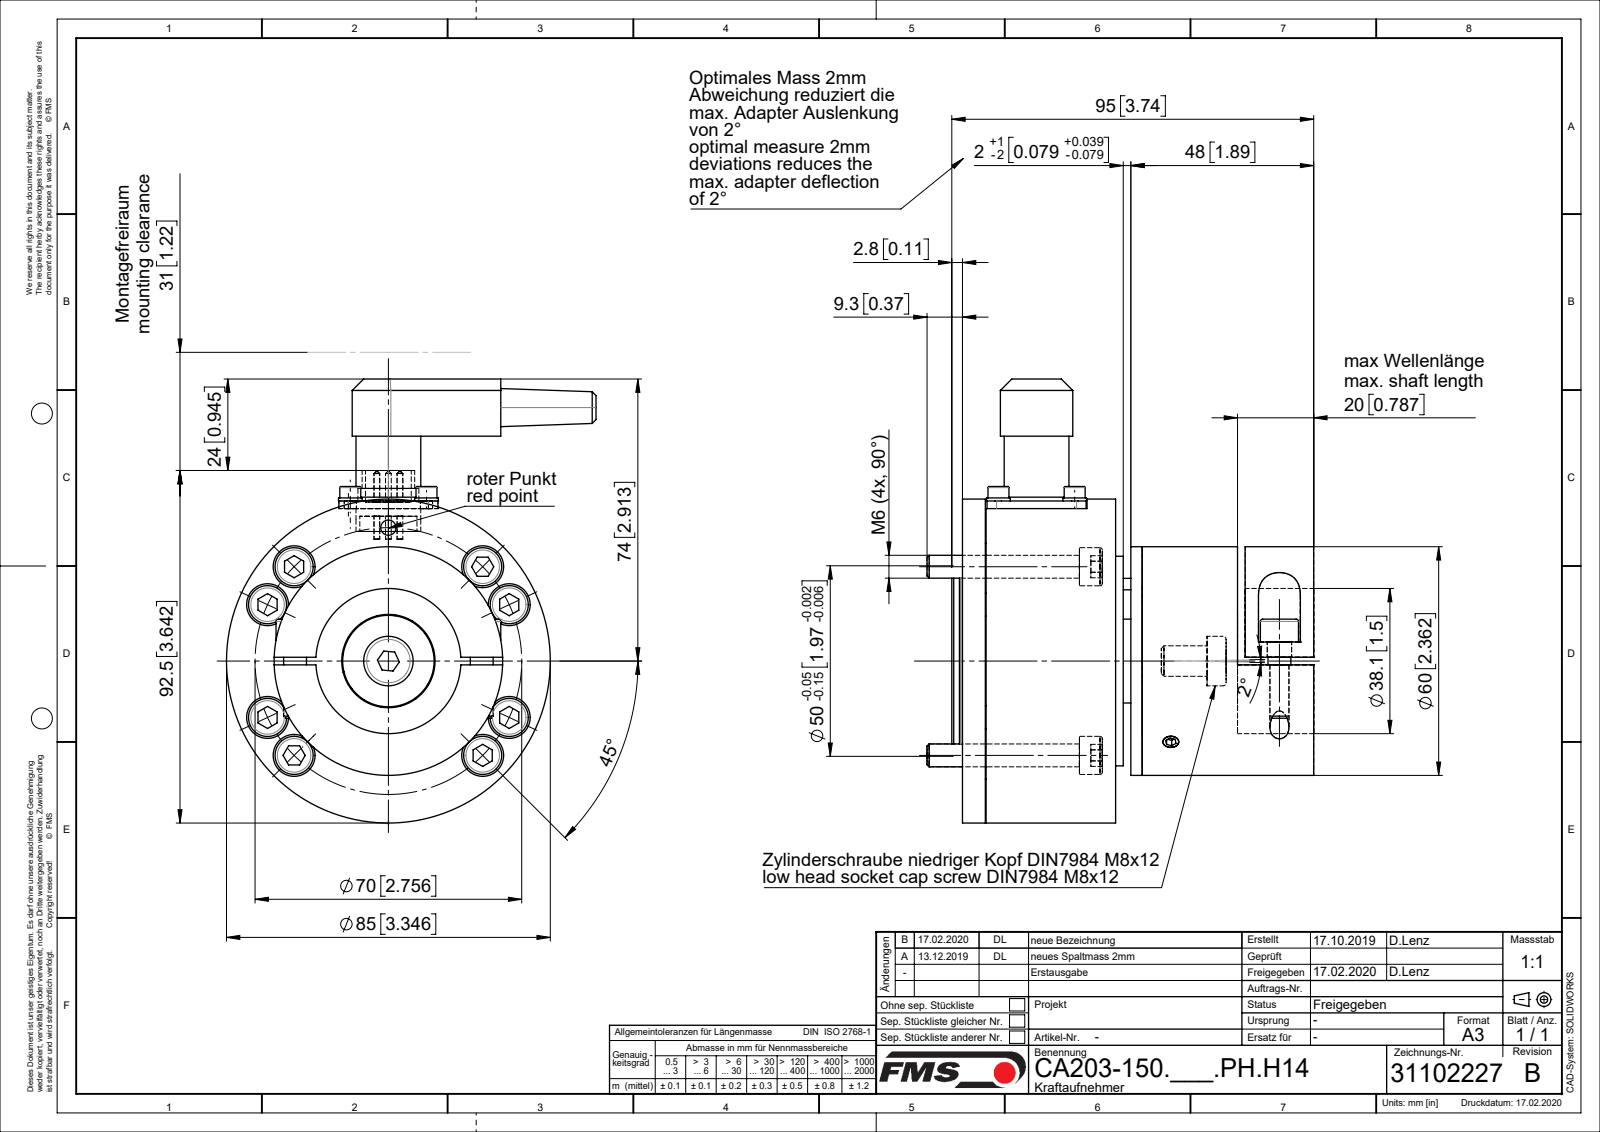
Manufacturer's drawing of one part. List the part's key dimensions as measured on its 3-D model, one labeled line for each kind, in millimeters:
Part name (STEP PRODUCT): ZEICHNUNG13; C50417_DI150; C0709081; C0612056 (+8 more)
STEP written by: Mechanical Desktop 2009 (CONFIG_CONTROL_DESIGN)
Units: millimetres
Bodies: 39 solids, 785 faces (278 planar, 354 cylindrical, 153 other)
Overall size (bounding box): 116.5 × 101 × 97
Volume: 303 992 mm³ · Surface area: 120 032 mm²
Round holes (diameter × count): ⌀2.6 ×8, ⌀6.5 ×8, ⌀11 ×8, ⌀5.15 ×6, ⌀2 ×5, ⌀3.2 ×4, ⌀3.6 ×4, ⌀4 ×4, ⌀7 ×4, ⌀6.4 ×2, ⌀3 ×1, ⌀4.33 ×1
Round bosses / shafts (diameter × count): ⌀6 ×14, ⌀10 ×10, ⌀3 ×8, ⌀1.5 ×5, ⌀6.2 ×4, ⌀5.5 ×4, ⌀5 ×4, ⌀85 ×1
Partial cylindrical surfaces — rounded edges, fillets, slot ends (radius × count): R4 ×10, R2.5 ×4, R5 ×2, R5.5 ×2, R9.5 ×1
Main face-to-face distances: 6, 11.5, 46.5, 2, 31.5, 1.5, 3, 6.5, 45, 16
Hole centre spacings: 24.78, 25.2, 56.46, 20, 32.8, 35, 51.14, 6
